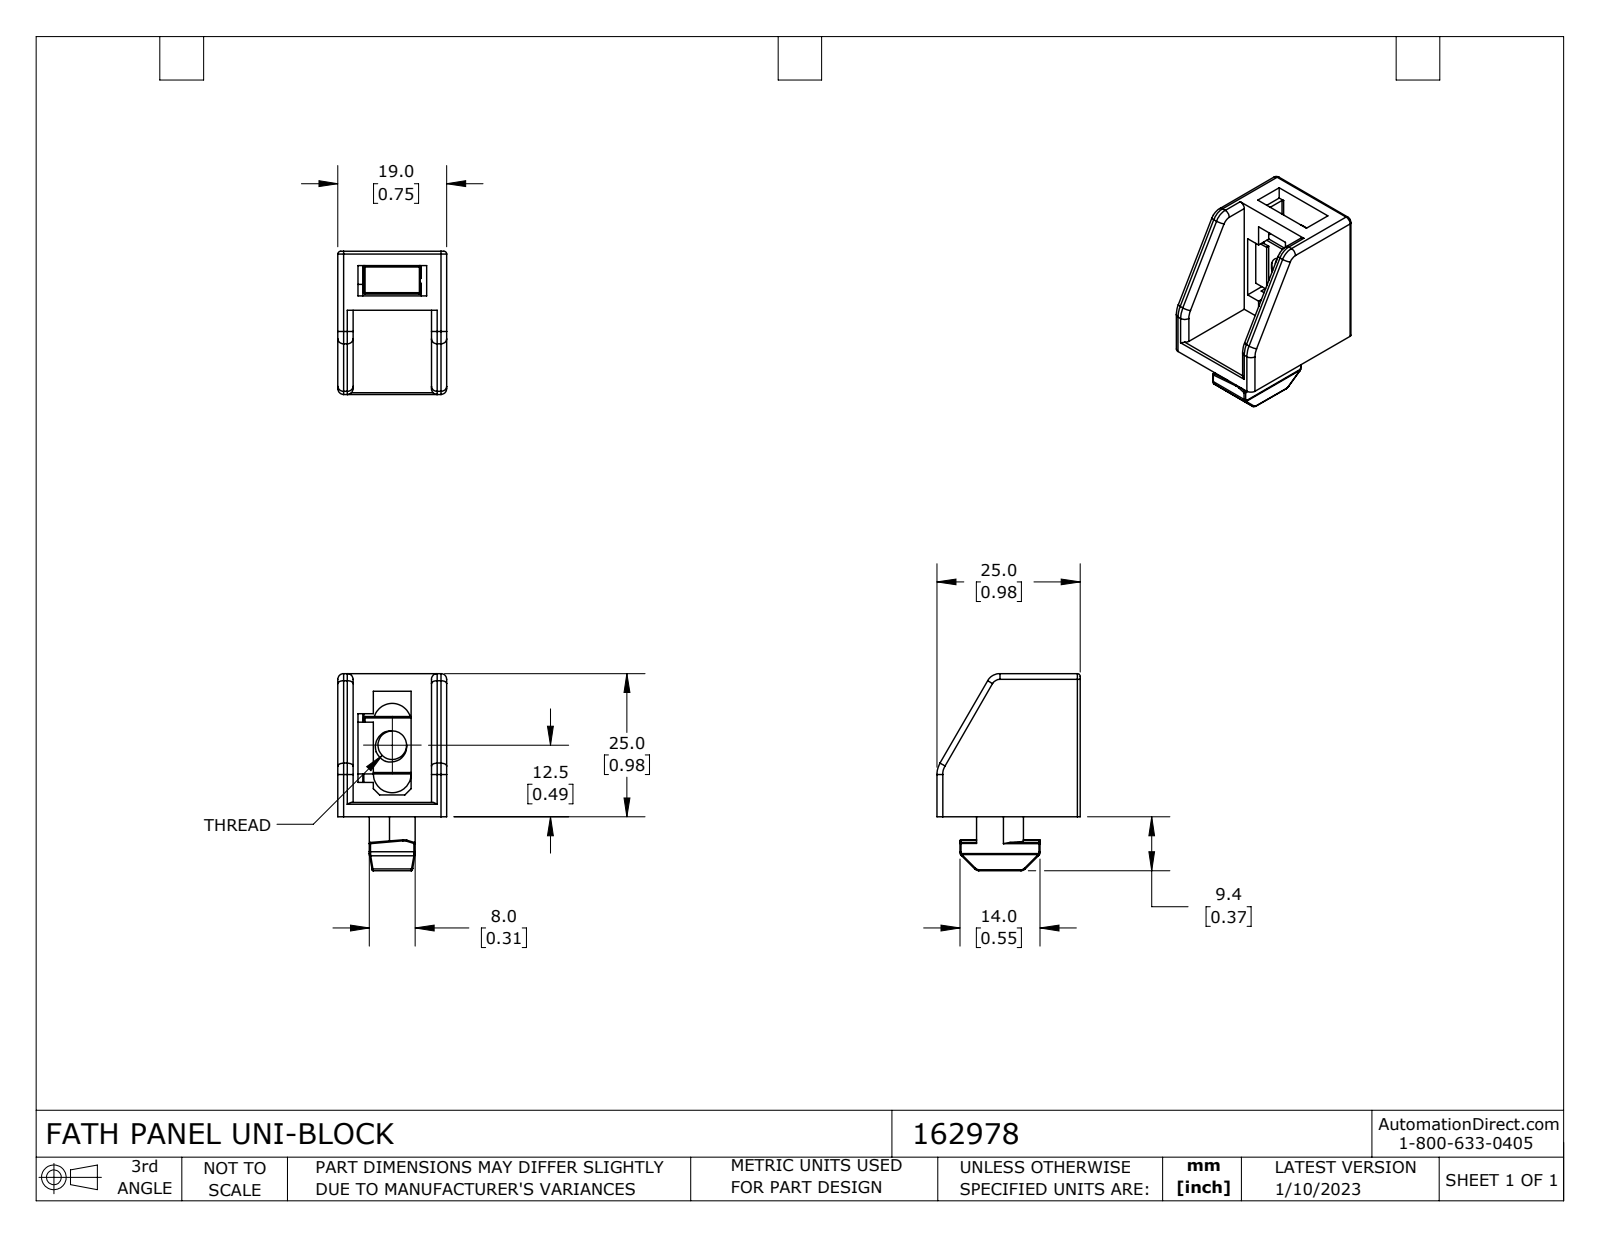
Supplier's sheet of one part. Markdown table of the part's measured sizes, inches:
| quantity | value |
| --- | --- |
| part name | 162978 |
| STEP written by | SolidWorks 2021 (CONFIG_CONTROL_DESIGN) |
| units | inches |
| bodies | 2 solids, 186 faces (63 planar, 80 cylindrical, 43 other) |
| overall size | 1.354 × 0.984 × 0.748 |
| volume | 0.375 in³ |
| surface area | 7.444 in² |
| round holes (diameter × count) | 0.079 × 2, 0.197 × 1 |
| partial cylindrical surfaces (radius × count) | 0.008 × 20, 0.039 × 18, 0.01 × 12, 0.02 × 3, 0.079 × 2, 0.13 × 2, 0.138 × 2, 0.012 × 1 |
| main face-to-face distances | 0.098, 0.748, 0.104, 0.644, 0.307, 0.539, 0.406, 0.067, 0.295, 0.033 |
| hole center spacings | 0.284, 0.472 |
